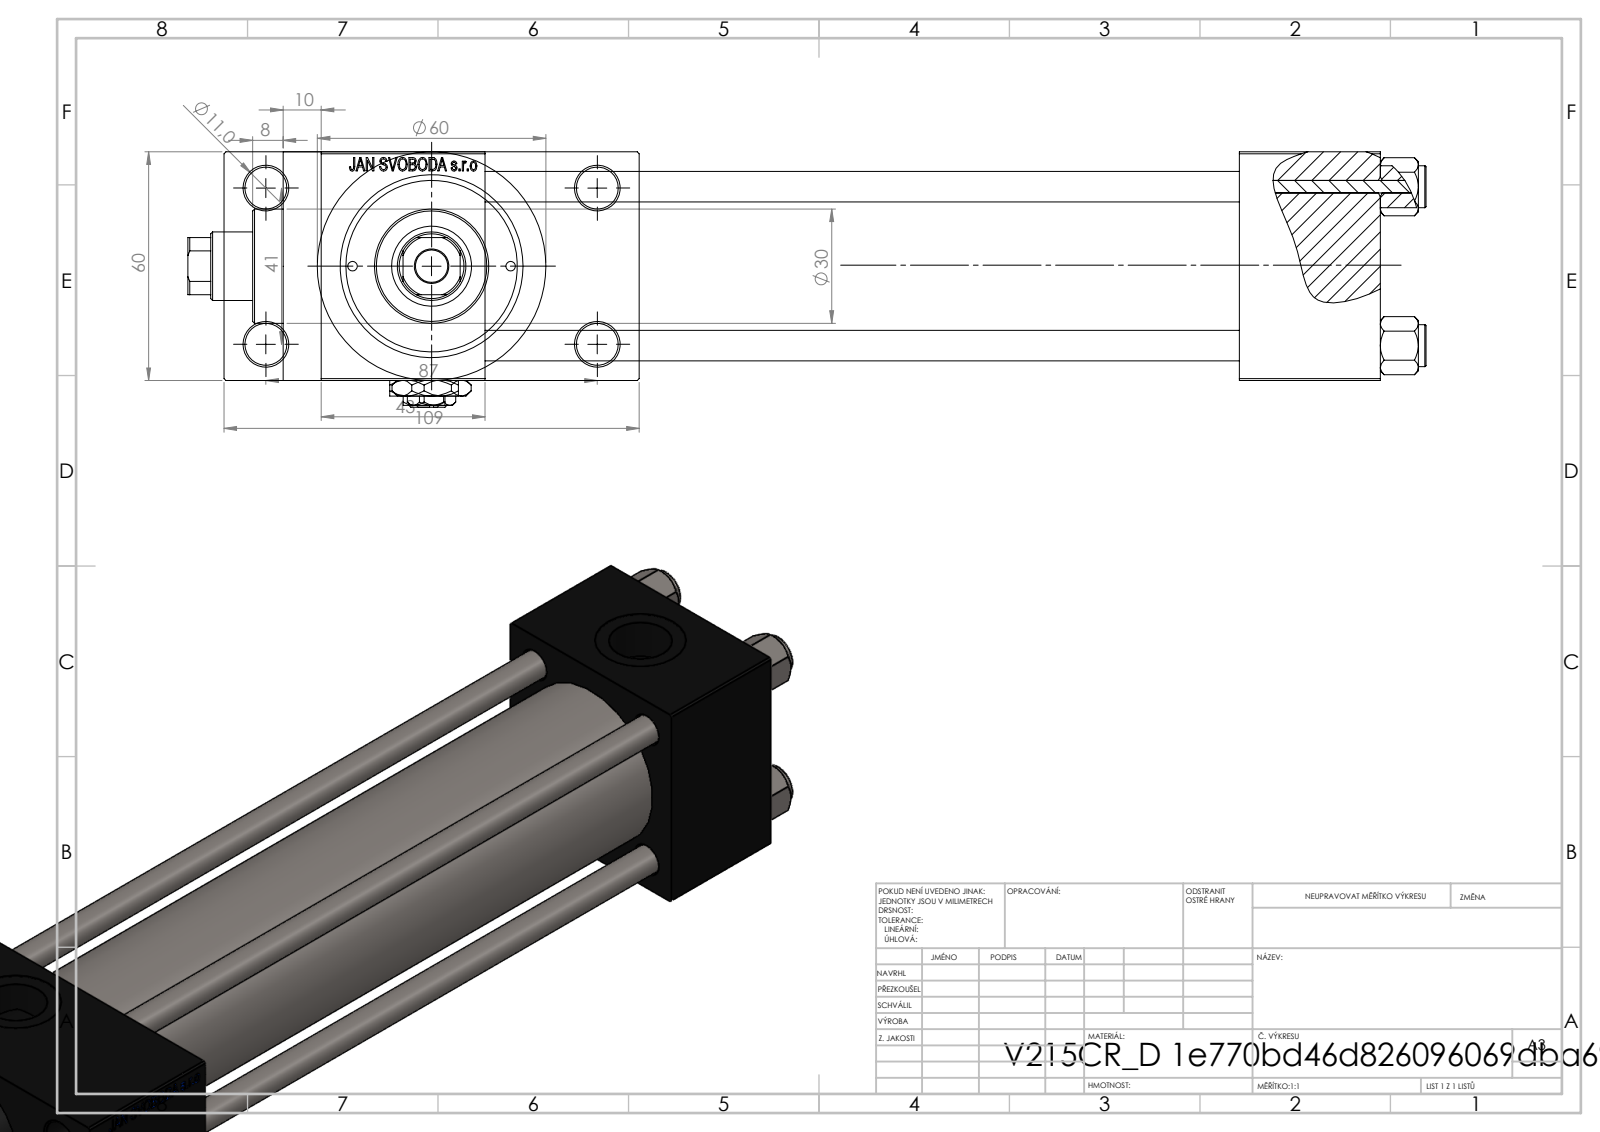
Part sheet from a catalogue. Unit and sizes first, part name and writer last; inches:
Units: inches
Overall size (bounding box): 12.795 × 4.291 × 2.638
Round holes (diameter × count): ⌀0.315 ×4, ⌀0.433 ×4, ⌀0.098 ×2, ⌀0.276 ×2, ⌀0.656 ×2, ⌀0.945 ×2, ⌀0.335 ×1, ⌀0.709 ×1, ⌀0.827 ×1, ⌀1.22 ×1, ⌀1.575 ×1, ⌀1.772 ×1
Round bosses / shafts (diameter × count): ⌀0.433 ×4, ⌀2.362 ×1, ⌀1.811 ×1, ⌀1.181 ×1
Partial cylindrical surfaces — rounded edges, fillets, slot ends (radius × count): R0.335 ×1
Main face-to-face distances: 2.362, 0.965, 3.327, 7.795, 1.457, 9.252, 1.693, 10.945, 9.488, 4.291
Hole centre spacings: 0.821, 0.892, 1.161, 1.206, 1.642, 1.832, 1.856, 1.893
Volume: 38.91 in³ · Surface area: 282 in²
Bodies: 12 solids, 1161 faces (524 planar, 97 cylindrical, 540 other)
Part name (STEP PRODUCT): V215CR_VCP_D; V215CR_D_TYCINKA; V215CR_D_Body; NUT_M5_D (+2 more)
STEP written by: SolidWorks 2019 (CONFIG_CONTROL_DESIGN)
